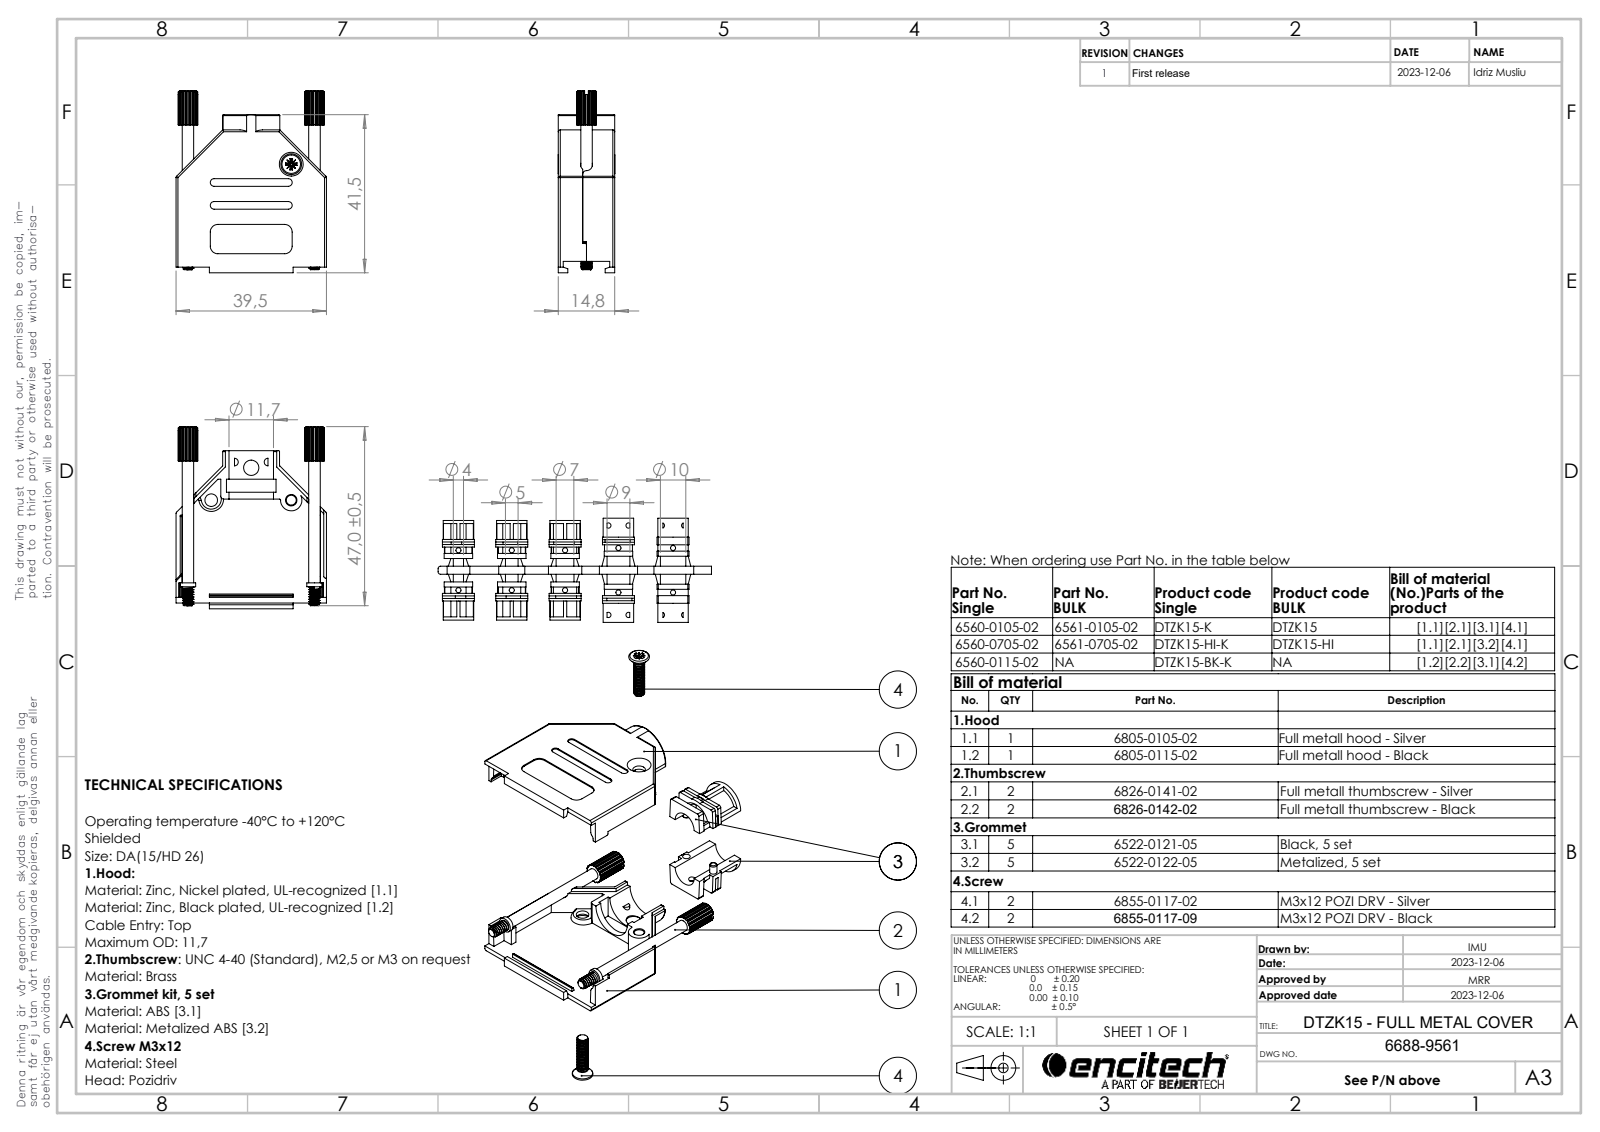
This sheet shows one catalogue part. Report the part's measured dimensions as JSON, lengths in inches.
{"part_name": "6805-0105-02; 6688-9561; 6826-0141-02; 6855-0117-02 (+1 more)", "step_written_by": "SolidWorks 2021 (AUTOMOTIVE_DESIGN)", "units": "inches", "bodies": {"solids": 8, "faces": 814, "planar": 432, "cylindrical": 306, "other": 76}, "overall_size": [1.882, 1.555, 0.585], "volume_in3": 0.478, "surface_area_in2": 18.69, "round_holes": [[0.079, 3], [0.102, 2], [0.122, 2], [0.13, 2], [0.157, 1], [0.276, 1], [0.461, 1]], "round_bosses_or_shafts": [[0.157, 2], [0.118, 2], [0.114, 2], [0.112, 2], [0.075, 2], [0.591, 1], [0.457, 1], [0.362, 1]], "partial_cylinders_radius": [[0.02, 24], [0.039, 12], [0.004, 8], [0.01, 8], [0.008, 6], [0.012, 4], [0.079, 4], [0.233, 4]], "face_to_face_distances": [0.051, 0.531, 0.583, 0.48, 0.24, 0.291, 0.039, 0.28, 0.063, 0.571], "hole_center_spacings": [0.225, 0.26, 0.274, 0.415, 0.532, 0.627, 0.654, 0.299]}
